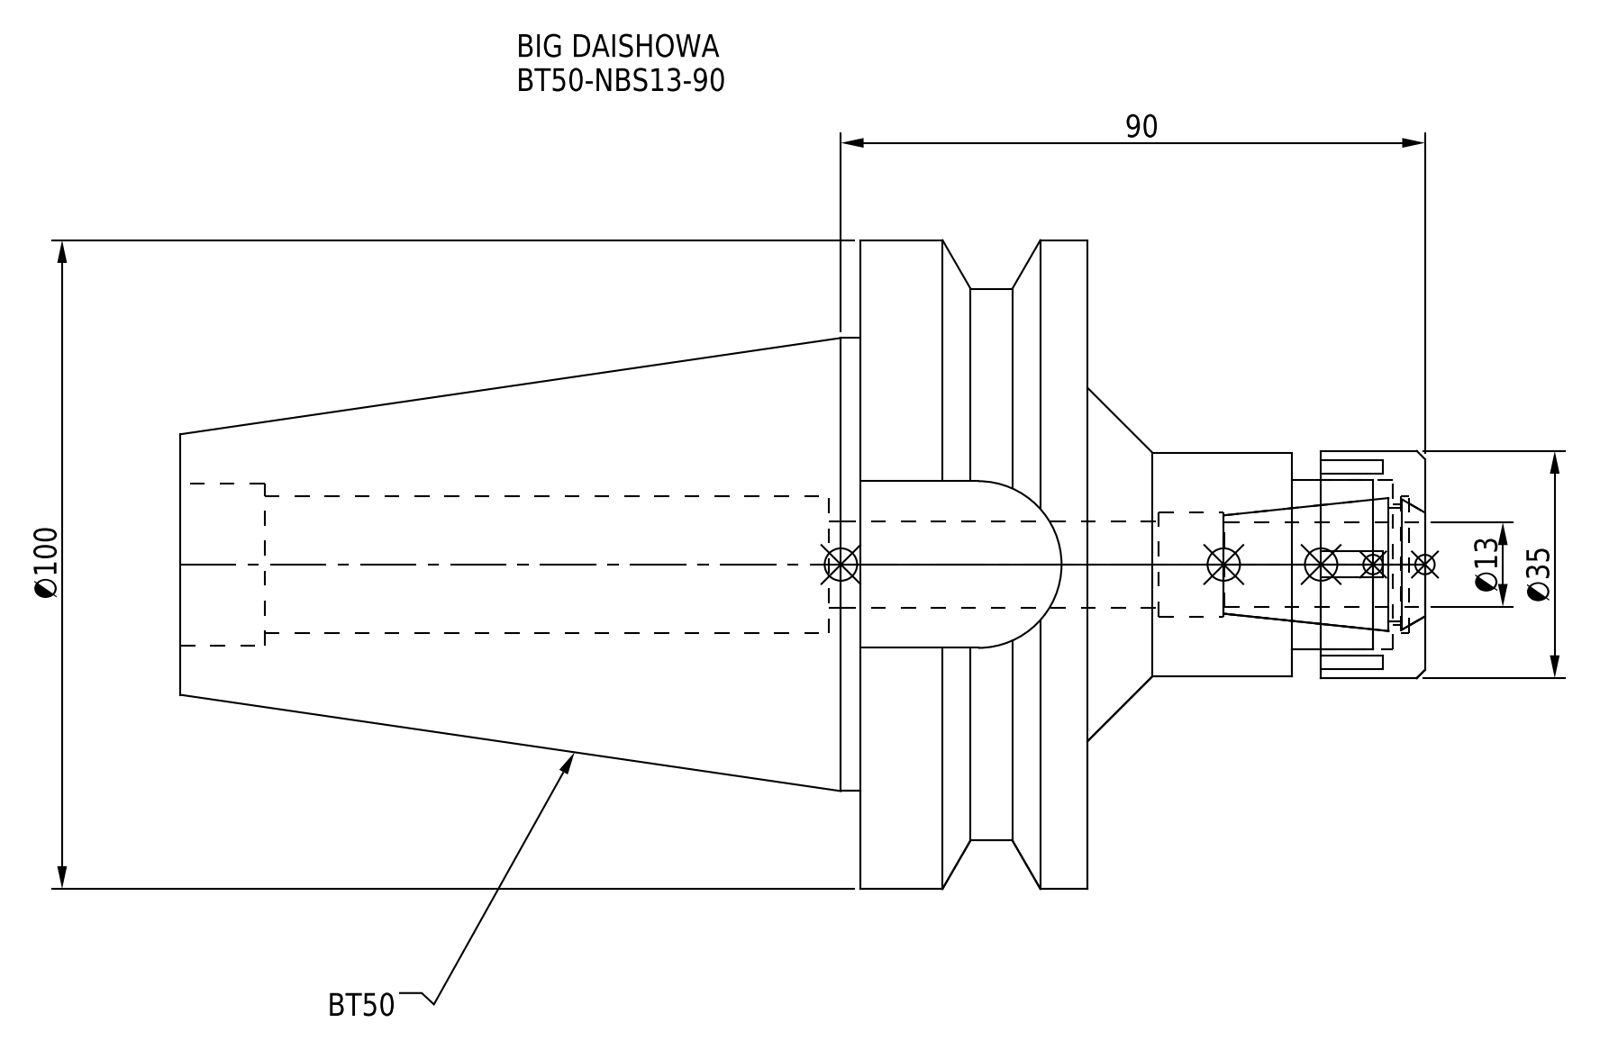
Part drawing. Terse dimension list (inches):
name: BT50-NBS13-90.stp; NBN13_1.stp; BT50-NBS13-90_2.stp; BT50-NBS13-90-FreeParts (+3 more)
written by: SolidWorks 2019 (CONFIG_CONTROL_DESIGN)
unit: in
bodies: 2 solids, 90 faces (44 planar, 32 cylindrical, 14 other)
size: 7.551 × 3.937 × 3.937
volume: 30.04 in³; area: 99.47 in²
holes: 1× ⌀0.524, 1× ⌀0.63, 1× ⌀0.728, 1× ⌀0.827, 1× ⌀0.835, 1× ⌀0.984, 1× ⌀1.024
bosses: 1× ⌀3.937, 1× ⌀3.346, 1× ⌀2.75, 1× ⌀1.378, 1× ⌀1.358
rounds: 1× R0.506
face distances: 1.378, 5.504, 4.126, 3.425, 2.787, 2.047, 7.551, 0.807, 1.417, 0.315
